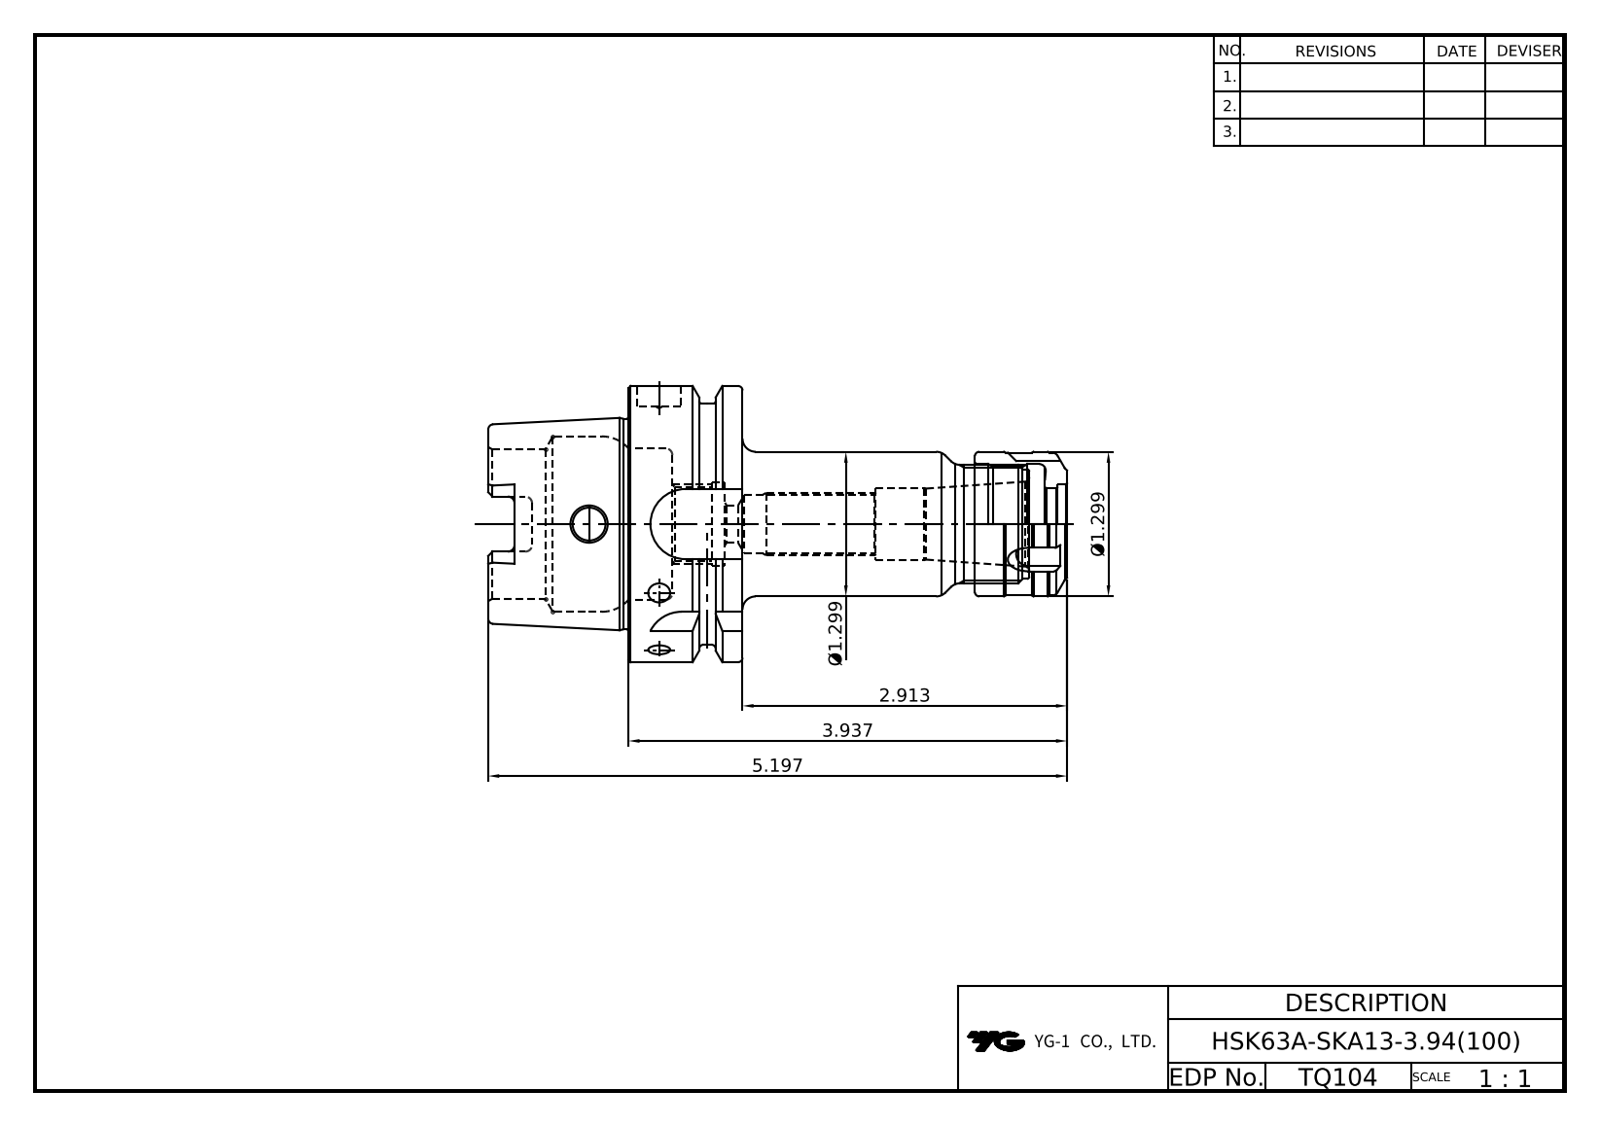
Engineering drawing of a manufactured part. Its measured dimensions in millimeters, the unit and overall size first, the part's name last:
Units: millimetres
Overall size (bounding box): 132 × 63 × 63
Round holes (diameter × count): ⌀7.5 ×1, ⌀8 ×1, ⌀10 ×1, ⌀12.57 ×1, ⌀16.2 ×1, ⌀16.5 ×1, ⌀16.92 ×1, ⌀18 ×1, ⌀19 ×1, ⌀25.92 ×1, ⌀27.4 ×1, ⌀34 ×1
Round bosses / shafts (diameter × count): ⌀63 ×1, ⌀55 ×1, ⌀48.04 ×1, ⌀33 ×1, ⌀32.6 ×1, ⌀27 ×1, ⌀25 ×1
Partial cylindrical surfaces — rounded edges, fillets, slot ends (radius × count): R1.5 ×6, R2.88 ×4, R8 ×4
Main face-to-face distances: 26, 16, 10, 32, 53, 42, 58, 4, 12, 22
Volume: 126 580 mm³ · Surface area: 36 260 mm²
Bodies: 2 solids, 201 faces (66 planar, 54 cylindrical, 81 other)
Part name (STEP PRODUCT): LO-HSK63A-SKA13-100; SKN13-NUT
STEP written by: Autodesk Inventor 2024 (AUTOMOTIVE_DESIGN)
